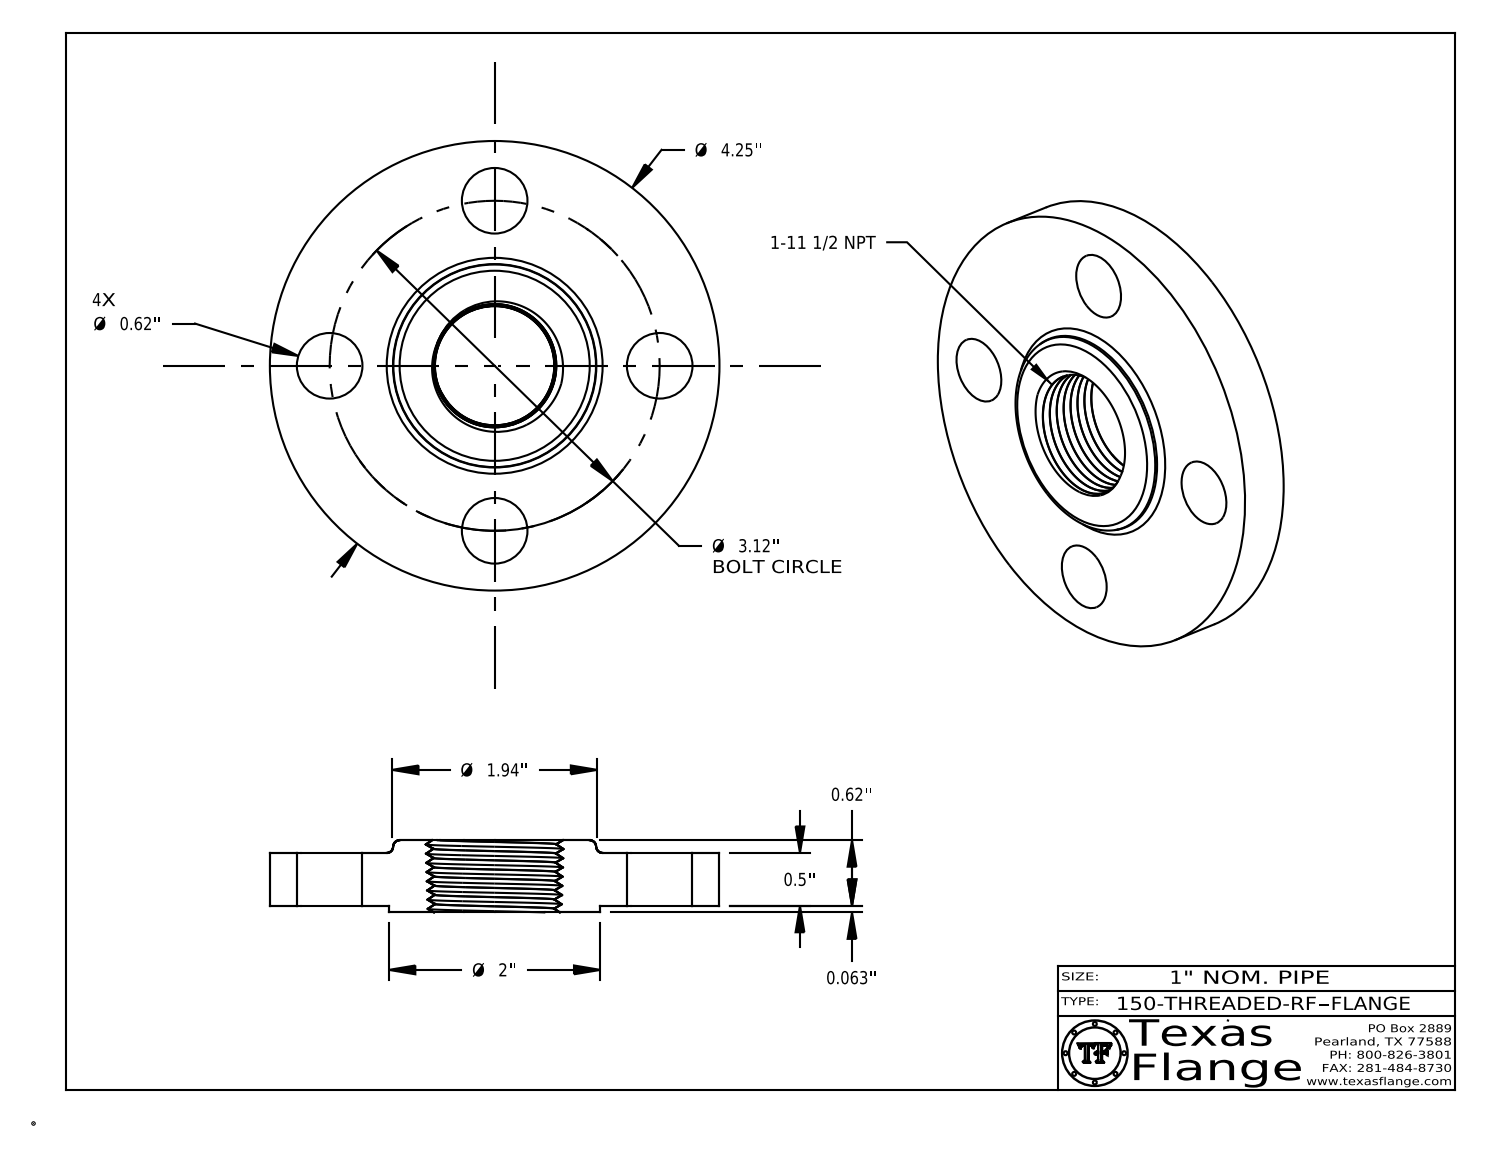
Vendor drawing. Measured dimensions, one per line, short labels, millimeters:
name: 150-THREADED-RF
written by: CATIA V5 STEP AP214 (AUTOMOTIVE_DESIGN)
unit: mm
bodies: 1 solid, 494 faces (369 planar, 32 cylindrical, 93 other)
size: 108 × 108 × 17.3
volume: 102 300 mm³; area: 25 790 mm²
holes: 4× ⌀15.7, 1× ⌀12.6
bosses: 8× ⌀0.8, 1× ⌀108, 1× ⌀50.8, 1× ⌀9.9
face distances: 12.7, 1.6, 14.3, 17.3, 15.7, 3, 13.9, 12.3, 0.4, 3.4
hole spacings: 56, 30.3, 73.2, 79.2
